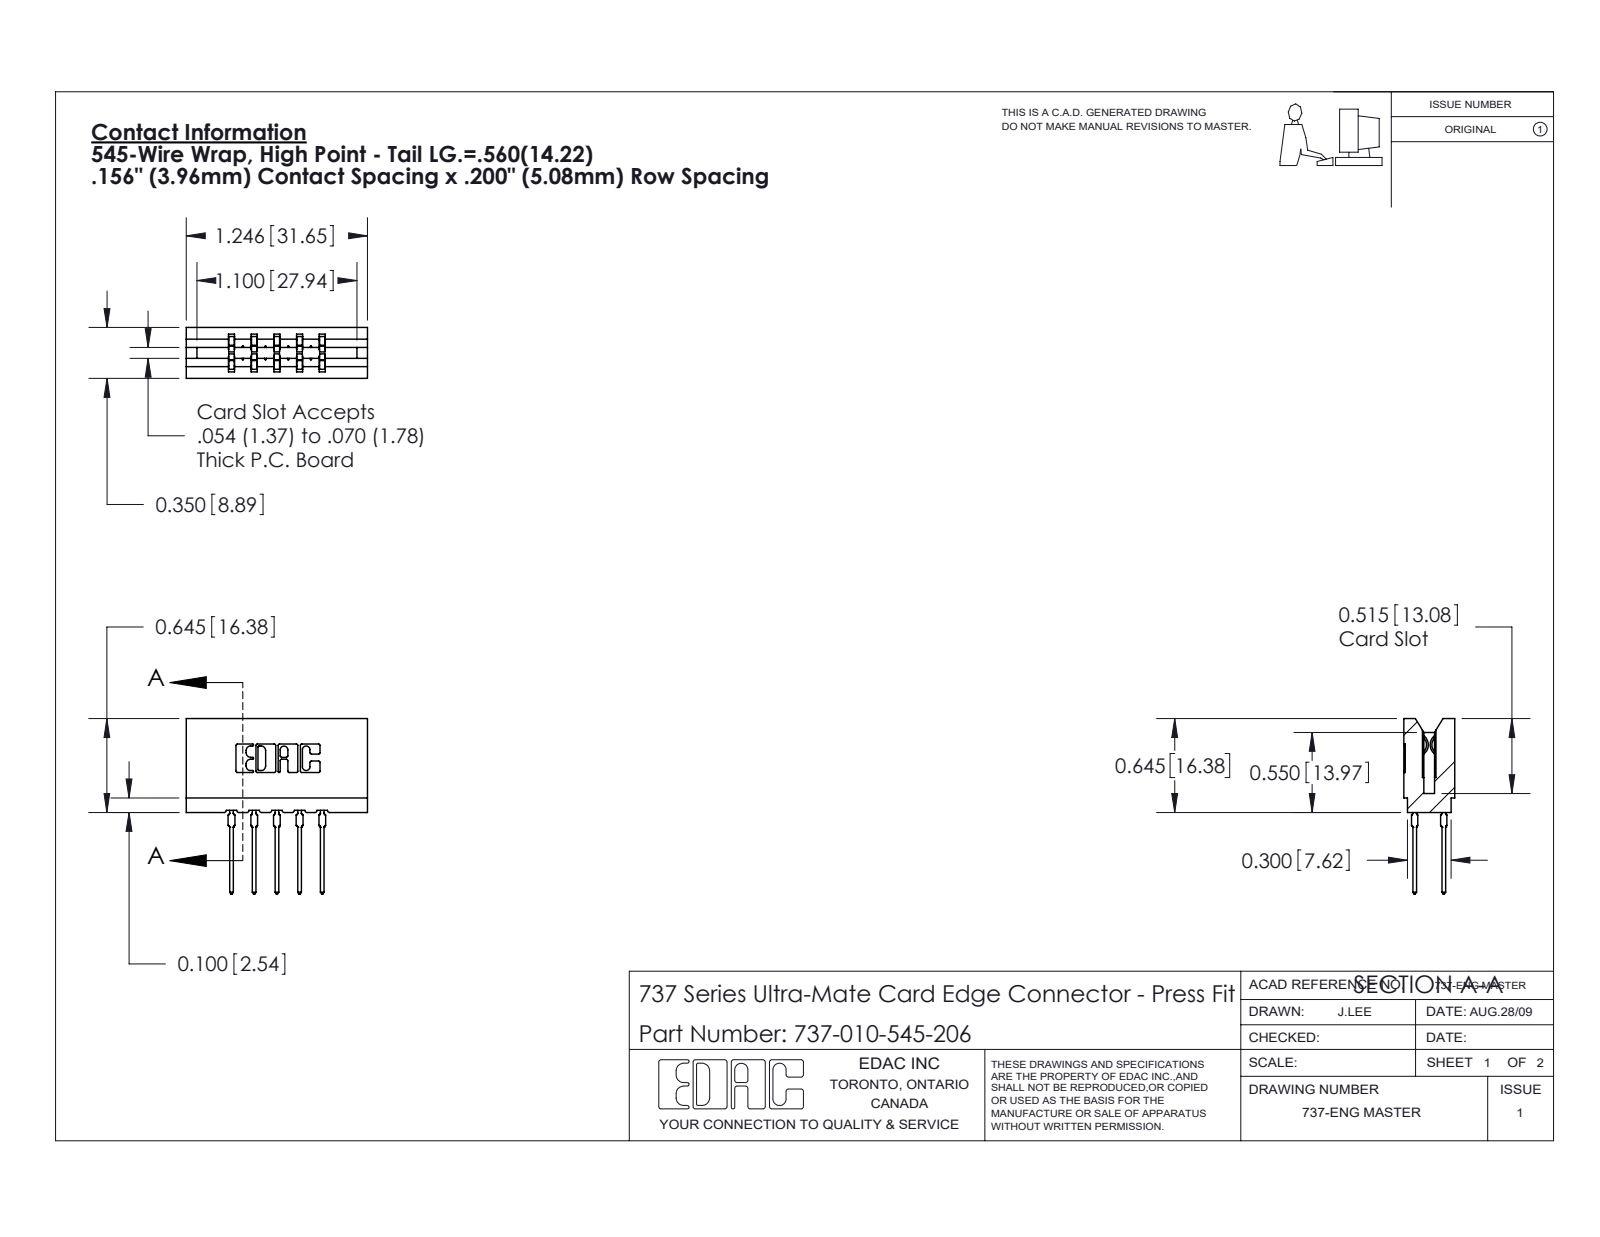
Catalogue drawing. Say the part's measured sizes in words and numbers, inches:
The part is named "745-292-001_545; 737-010-545-206; 737 Part_Insulator Option - 06". Its 3-D file was written by "SolidWorks 2020 (CONFIG_CONTROL_DESIGN)". It is 11 solids with 995 faces: 520 planar, 215 cylindrical and 260 other. Overall it measures 1.246 by 1.206 by 0.35 inches. Its volume is 0.206 cubic inches and its surface area 6.612 square inches. Partial cylindrical surfaces (rounded edges, fillets, slot ends): 22 of radius 0.01, 20 of radius 0.021, 10 of radius 0.015, 8 of radius 0.005, 8 of radius 0.011, 6 of radius 0.007, 6 of radius 0.031, 3 of radius 0.026. The main face-to-face distances are 0.138, 0.212, 0.156, 0.35, 0.312, 0.198, 0.074, 0.063, 0.287, 0.076.
